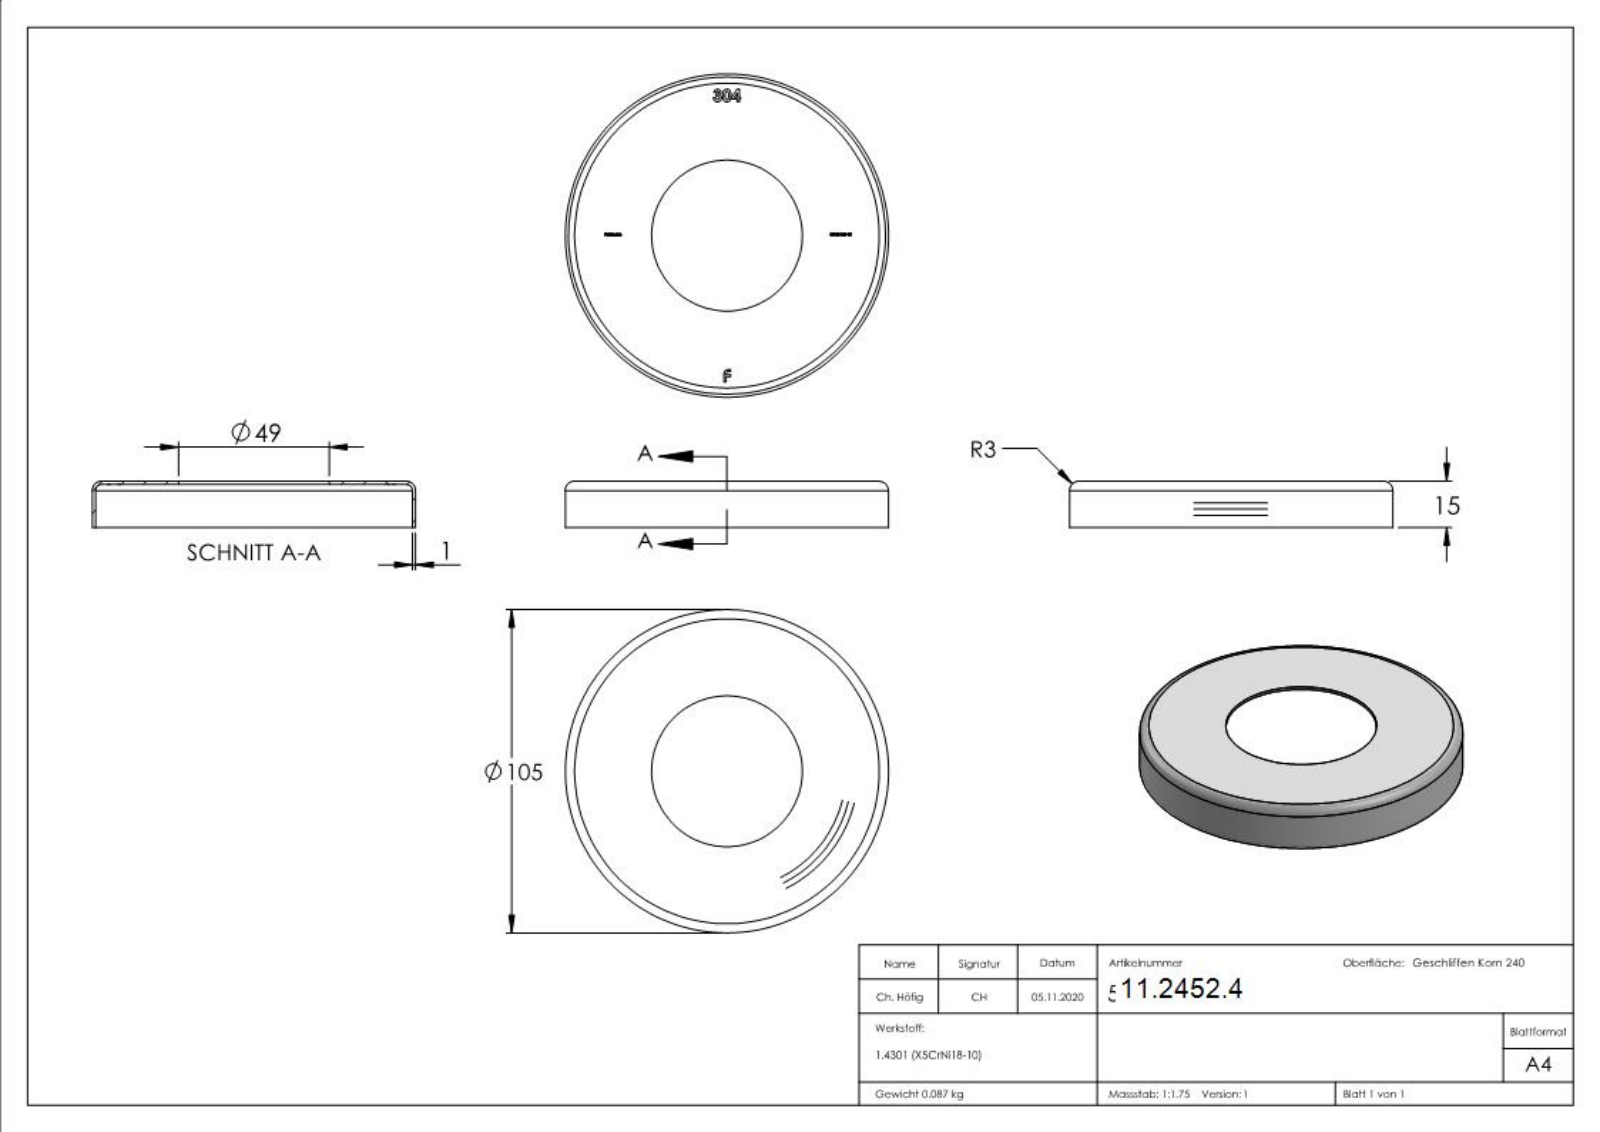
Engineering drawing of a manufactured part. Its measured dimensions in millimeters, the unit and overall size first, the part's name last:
Units: millimetres
Overall size (bounding box): 105 × 105 × 15
Round holes (diameter × count): ⌀49 ×1, ⌀103 ×1
Round bosses / shafts (diameter × count): ⌀105 ×1
Main face-to-face distances: 1, 14, 15, 14.1, 0.9, 0.71, 5, 4.31, 43.52, 4.29
Volume: 10 991 mm³ · Surface area: 22 483 mm²
Bodies: 1 solid, 321 faces (176 planar, 6 cylindrical, 139 other)
Part name (STEP PRODUCT): 50153-240-15
STEP written by: SolidWorks 2018 (CONFIG_CONTROL_DESIGN)
